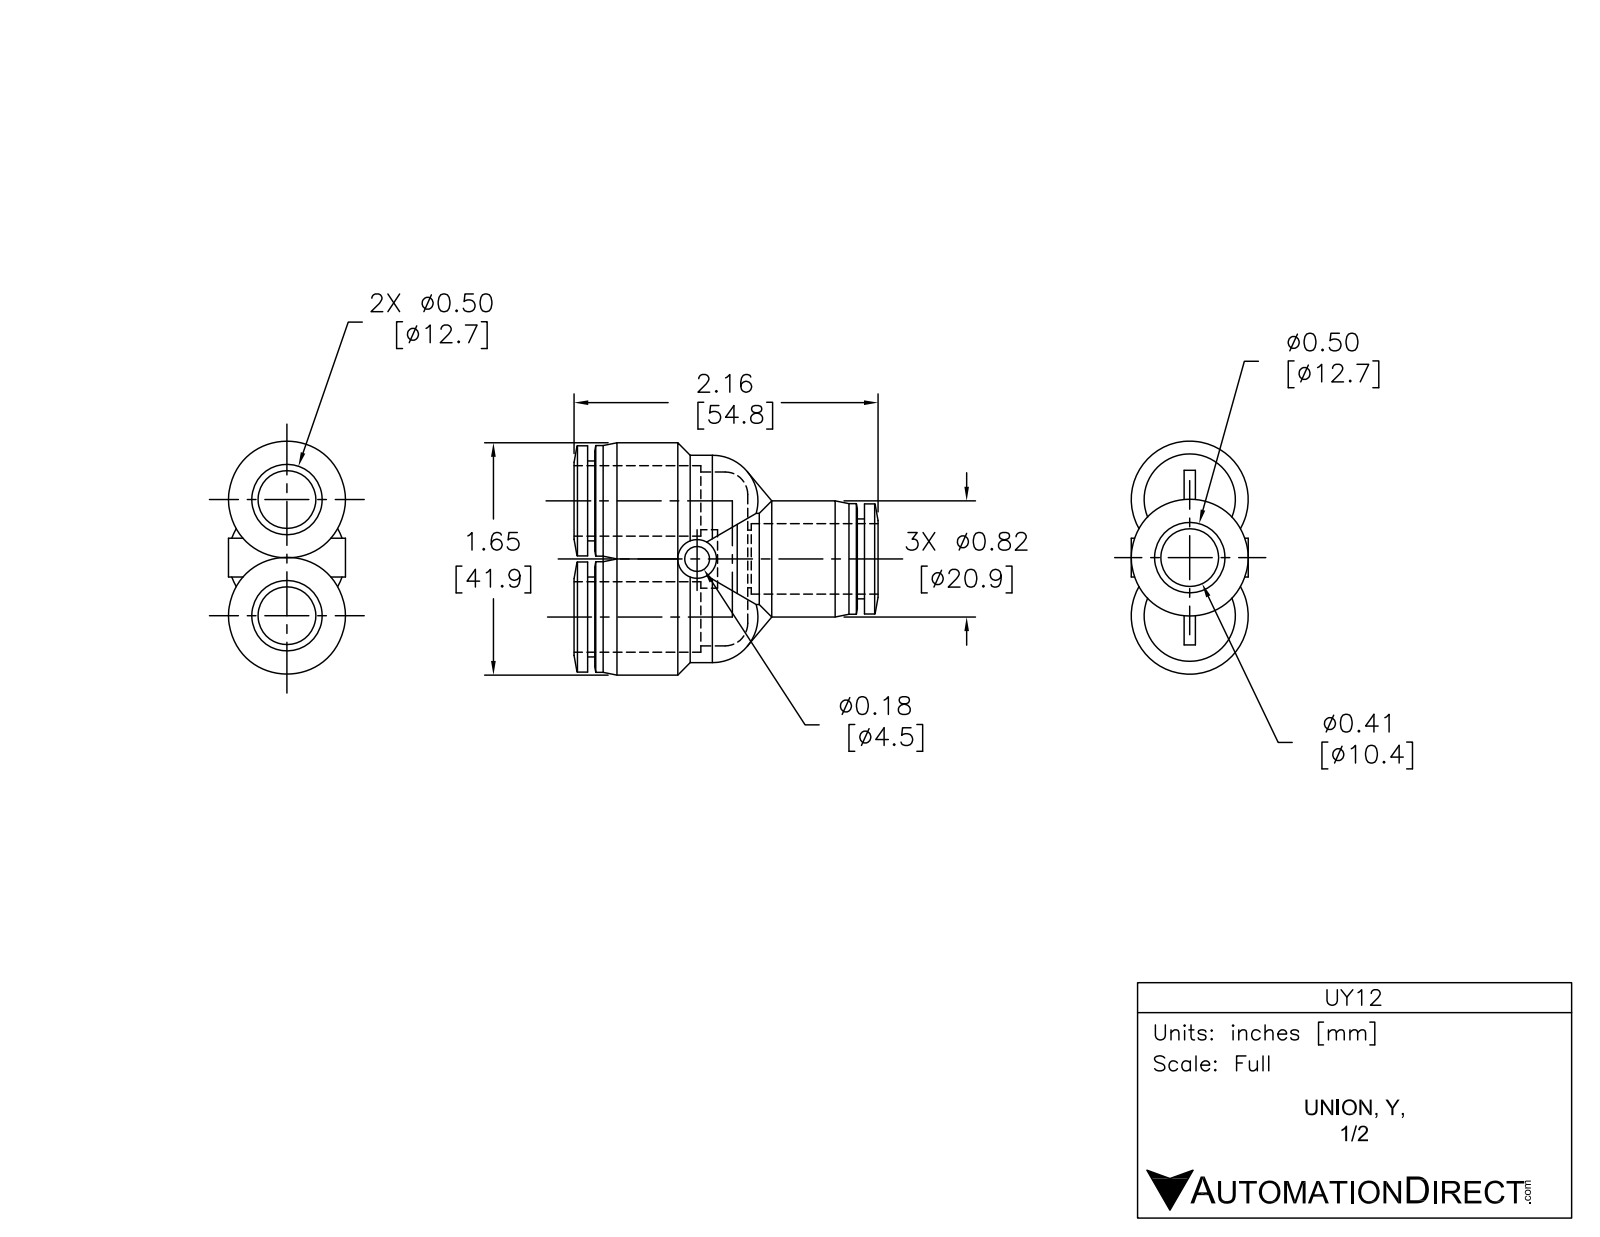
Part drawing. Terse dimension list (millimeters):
name: UY12
written by: SolidWorks 2015 (AUTOMOTIVE_DESIGN)
unit: mm
bodies: 1 solid, 108 faces (18 planar, 40 cylindrical, 50 other)
size: 54.5 × 42 × 21
volume: 16 000 mm³; area: 10 660 mm²
holes: 3× ⌀13, 1× ⌀4.5
bosses: 3× ⌀21, 3× ⌀20, 3× ⌀19.9, 3× ⌀16.5, 3× ⌀14.5, 1× ⌀7
face distances: 20.5, 1.3, 19.3, 29.1, 48.3, 27.8, 49.6, 8.5, 47, 9
hole spacings: 10.5, 21
